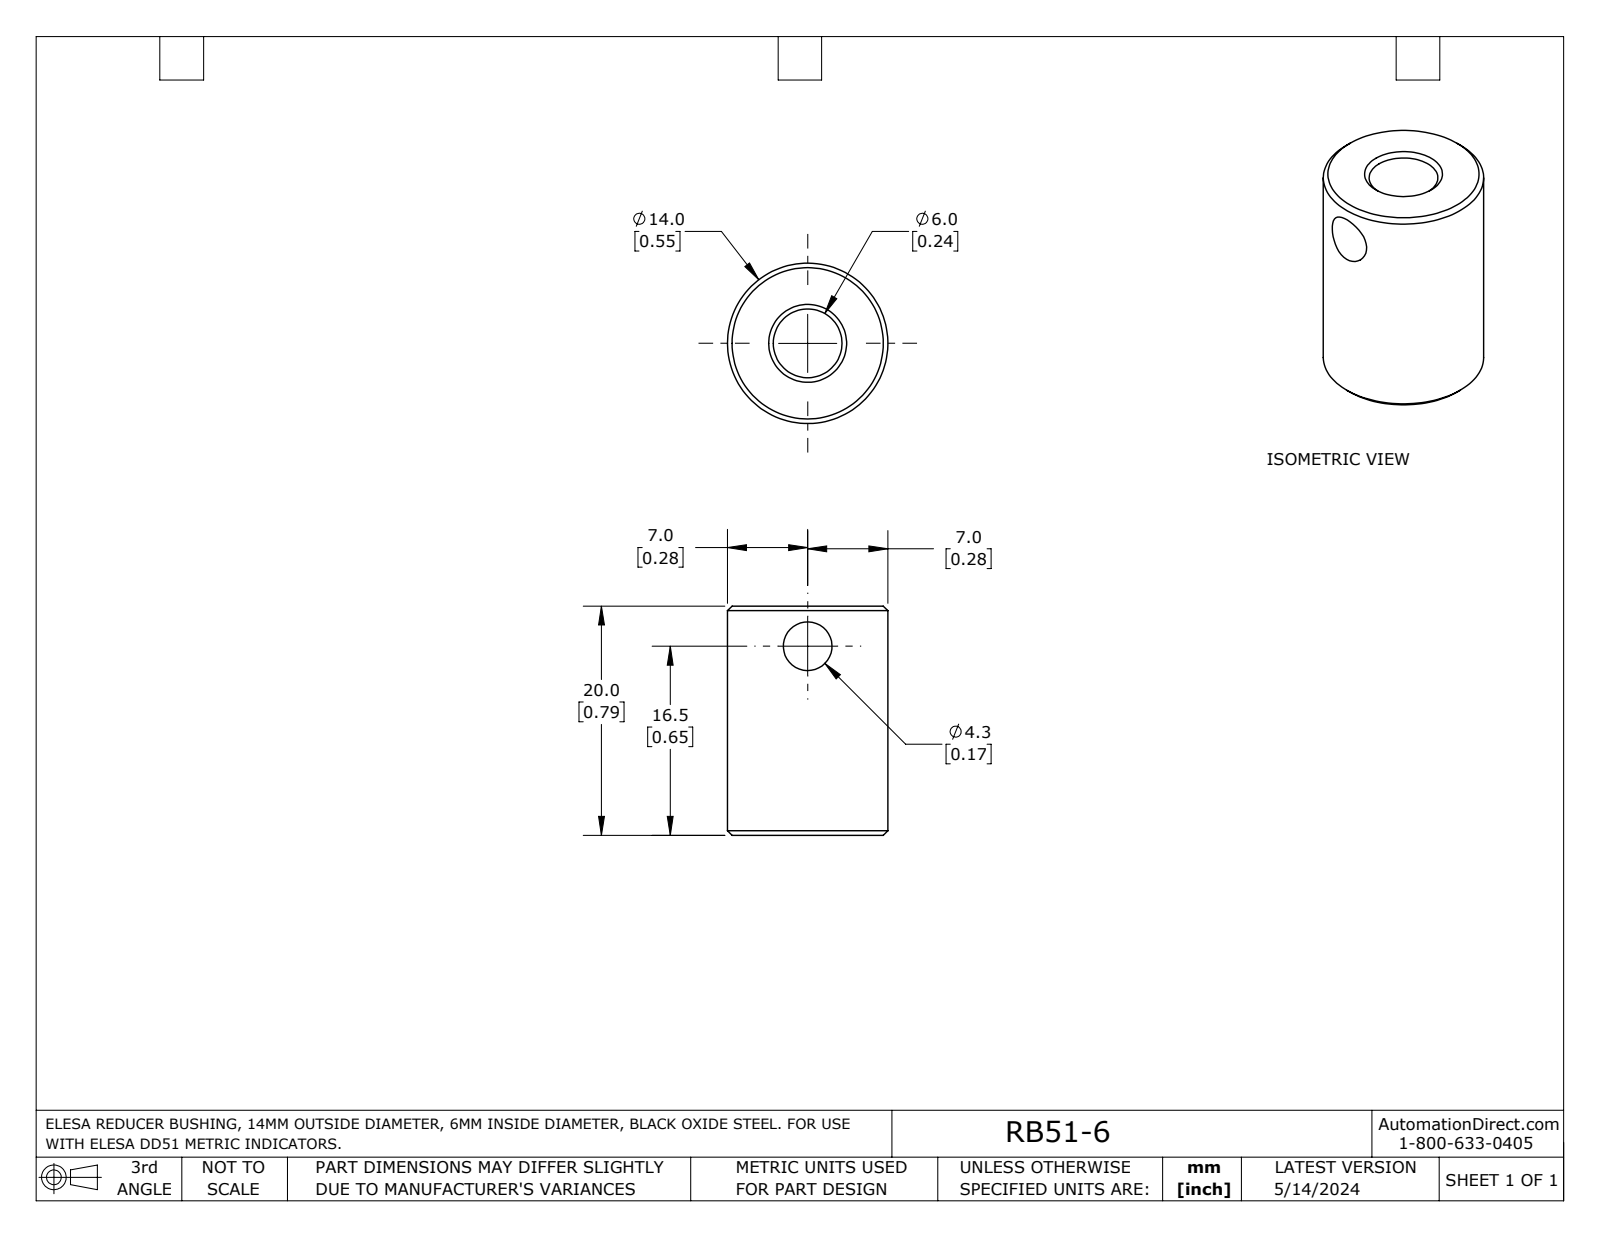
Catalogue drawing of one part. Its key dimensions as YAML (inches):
part_name: "RB51-6"
step_written_by: "SolidWorks 2023 (AUTOMOTIVE_DESIGN)"
units: inches
bodies: {solids: 1, faces: 9, planar: 2, cylindrical: 3, other: 4}
overall_size: [0.787, 0.551, 0.551]
volume: 0.149
surface_area: 2.334
round_holes:
  - {diameter: 0.167, count: 1}
  - {diameter: 0.236, count: 1}
round_bosses_or_shafts:
  - {diameter: 0.551, count: 1}
face_to_face_distances: [0.787]
